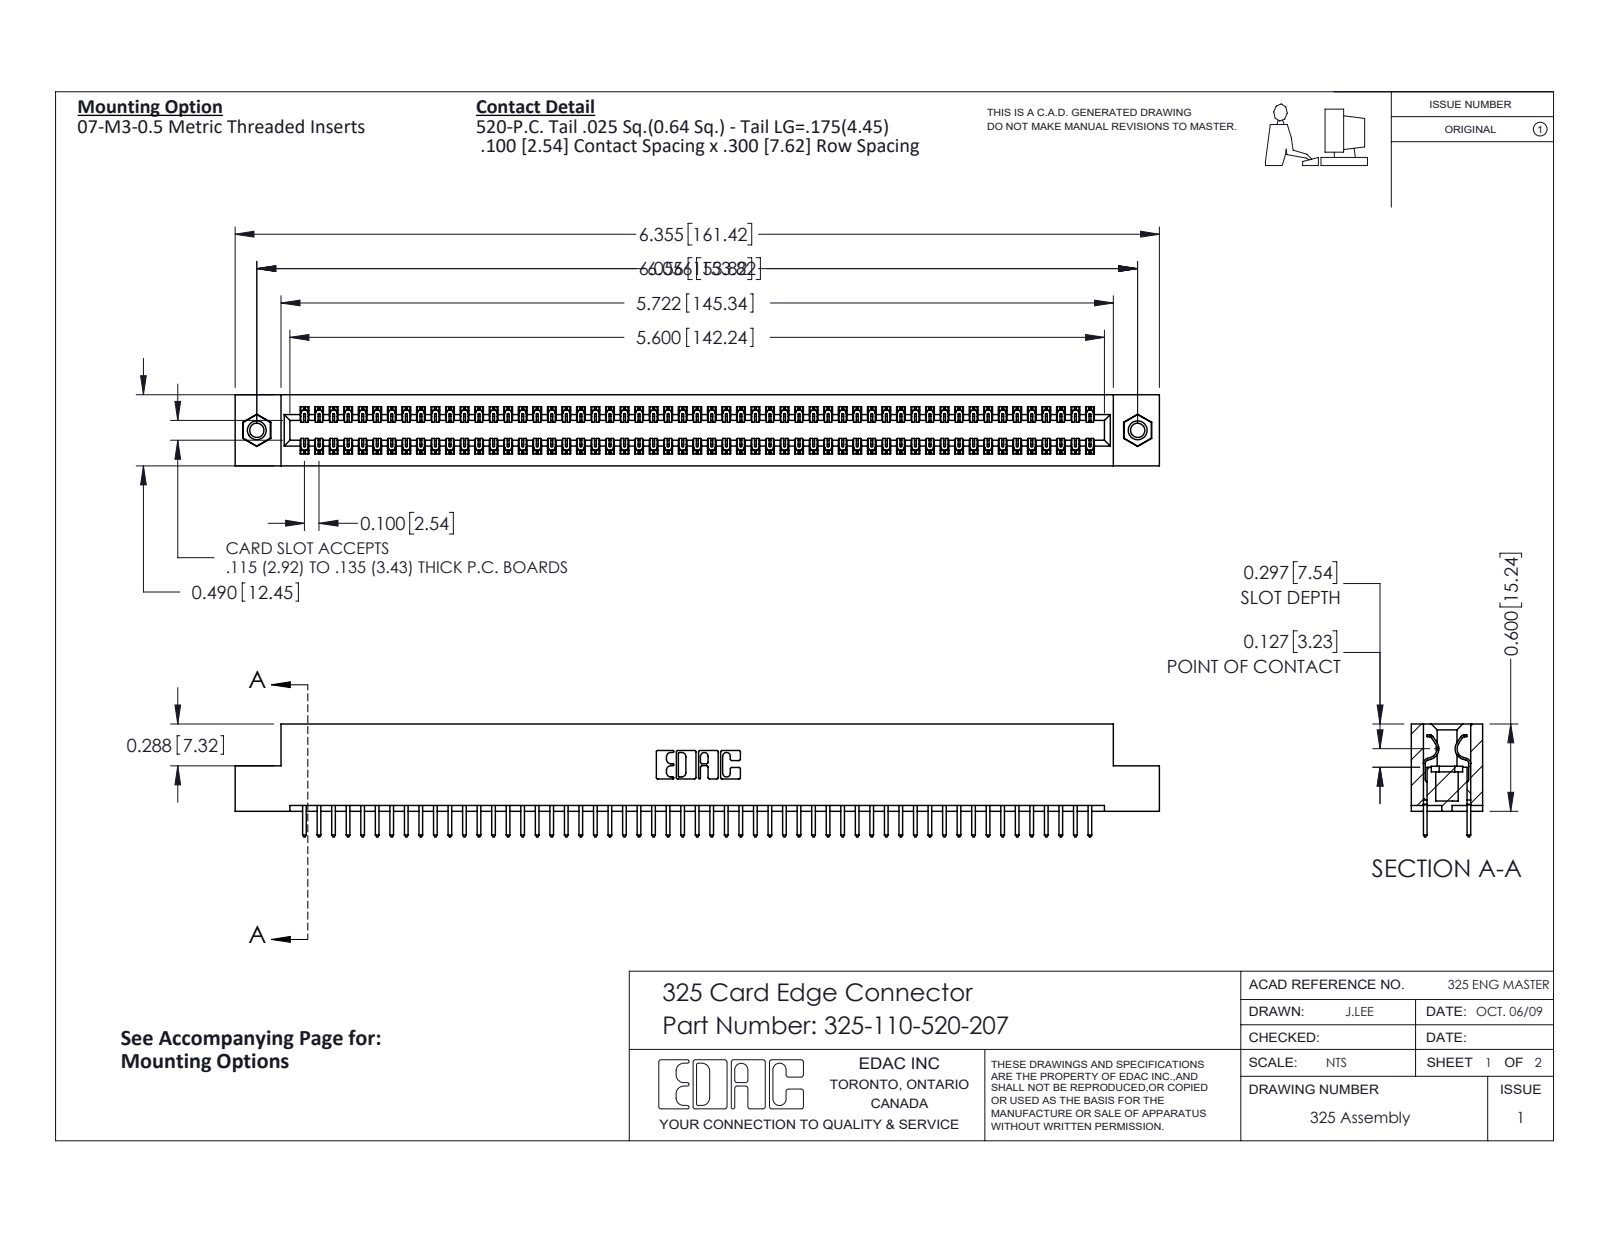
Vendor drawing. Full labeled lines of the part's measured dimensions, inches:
Part name (STEP PRODUCT): 345-250-001_345-250-005-103; 325 Part_TI; 325-110-520-207; 325-292-001_325-293-120
STEP written by: SolidWorks 2016 (CONFIG_CONTROL_DESIGN)
Units: inches
Bodies: 113 solids, 5894 faces (4062 planar, 1816 cylindrical, 16 other)
Overall size (bounding box): 6.355 × 0.775 × 0.49
Volume: 1.277 in³ · Surface area: 39.43 in²
Round holes (diameter × count): ⌀0.098 ×2, ⌀0.125 ×2, ⌀0.16 ×2
Round bosses / shafts (diameter × count): ⌀0.155 ×2
Partial cylindrical surfaces — rounded edges, fillets, slot ends (radius × count): R0.006 ×165, R0.01 ×110, R0.01 ×22, R0.007 ×6, R0.031 ×6, R0.026 ×3, R0.014 ×2, R0.022 ×2
Main face-to-face distances: 0.083, 0.407, 0.49, 0.3, 0.107, 0.383, 0.025, 0.325, 0.275, 0.263
Hole centre spacings: 6.056
